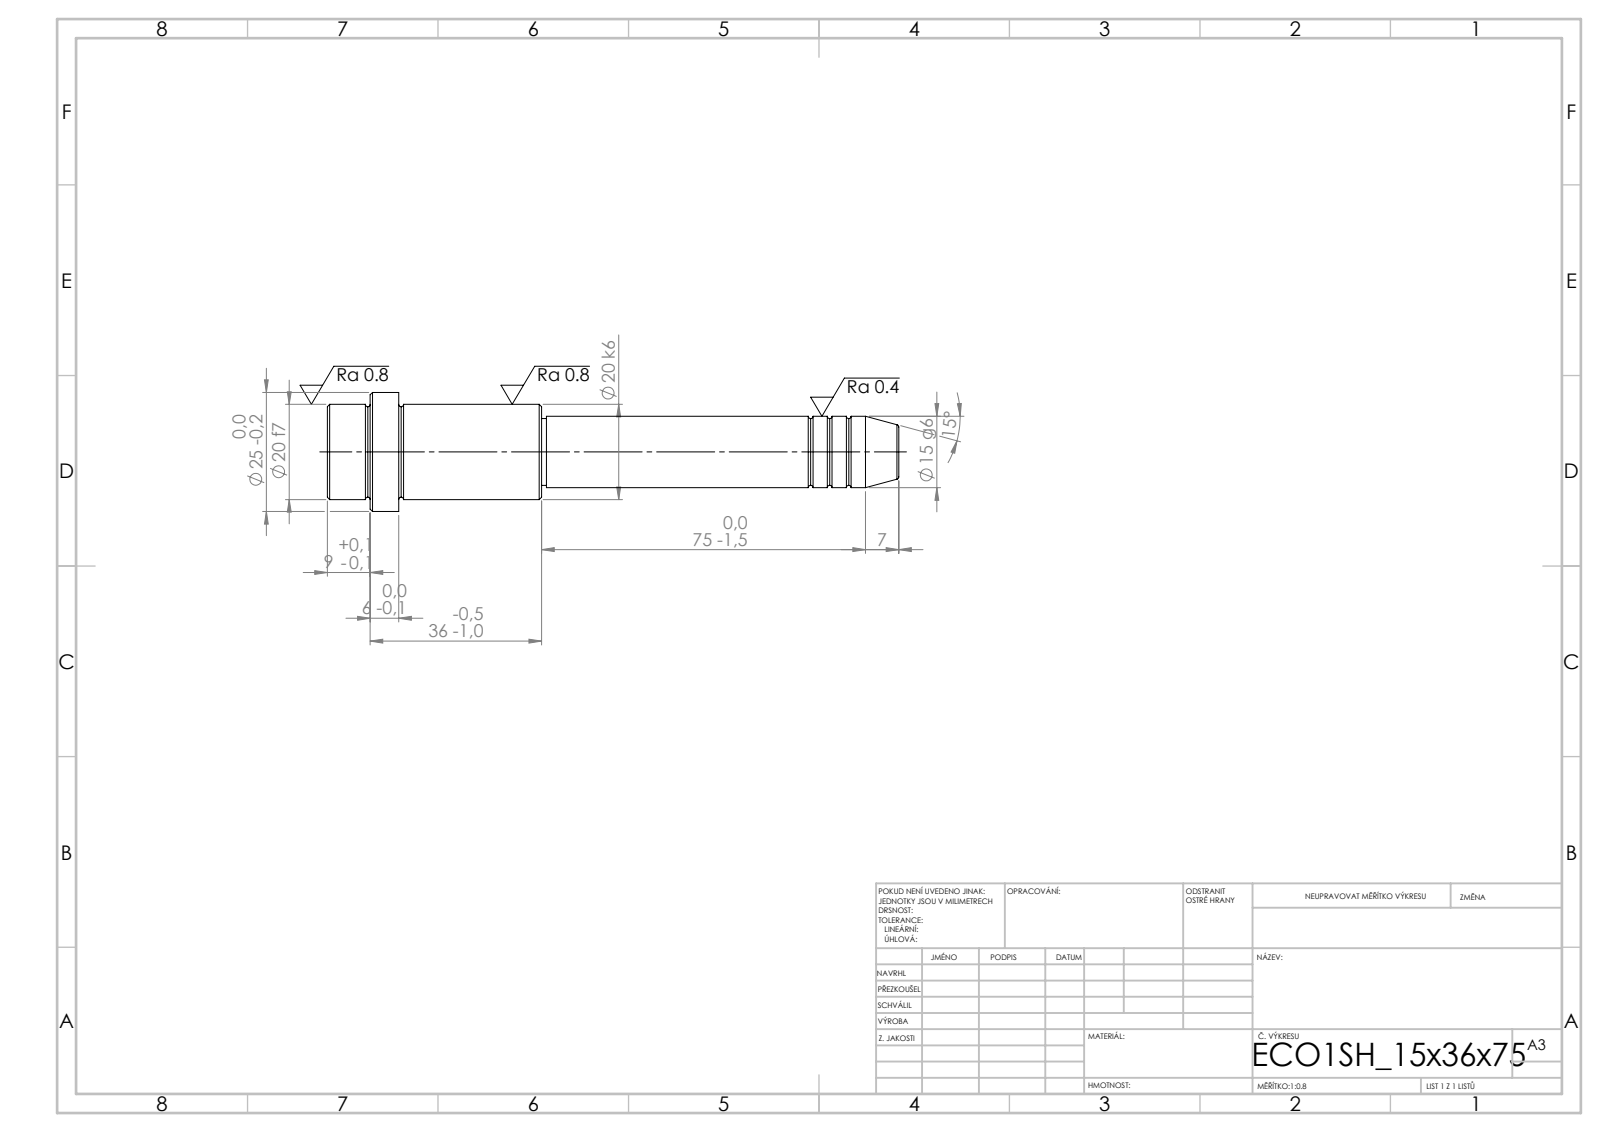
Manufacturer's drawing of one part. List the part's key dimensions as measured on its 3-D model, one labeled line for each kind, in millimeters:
STEP written by: SolidWorks 2019 (CONFIG_CONTROL_DESIGN)
Units: millimetres
Bodies: 1 solid, 52 faces (6 planar, 16 cylindrical, 30 other)
Overall size (bounding box): 120 × 25 × 25
Volume: 28 016 mm³ · Surface area: 7 444 mm²
Round bosses / shafts (diameter × count): ⌀25 ×1, ⌀20 ×1, ⌀15 ×1, ⌀14 ×1
Main face-to-face distances: 15, 6, 9, 30, 36, 45, 75, 105, 111, 120
